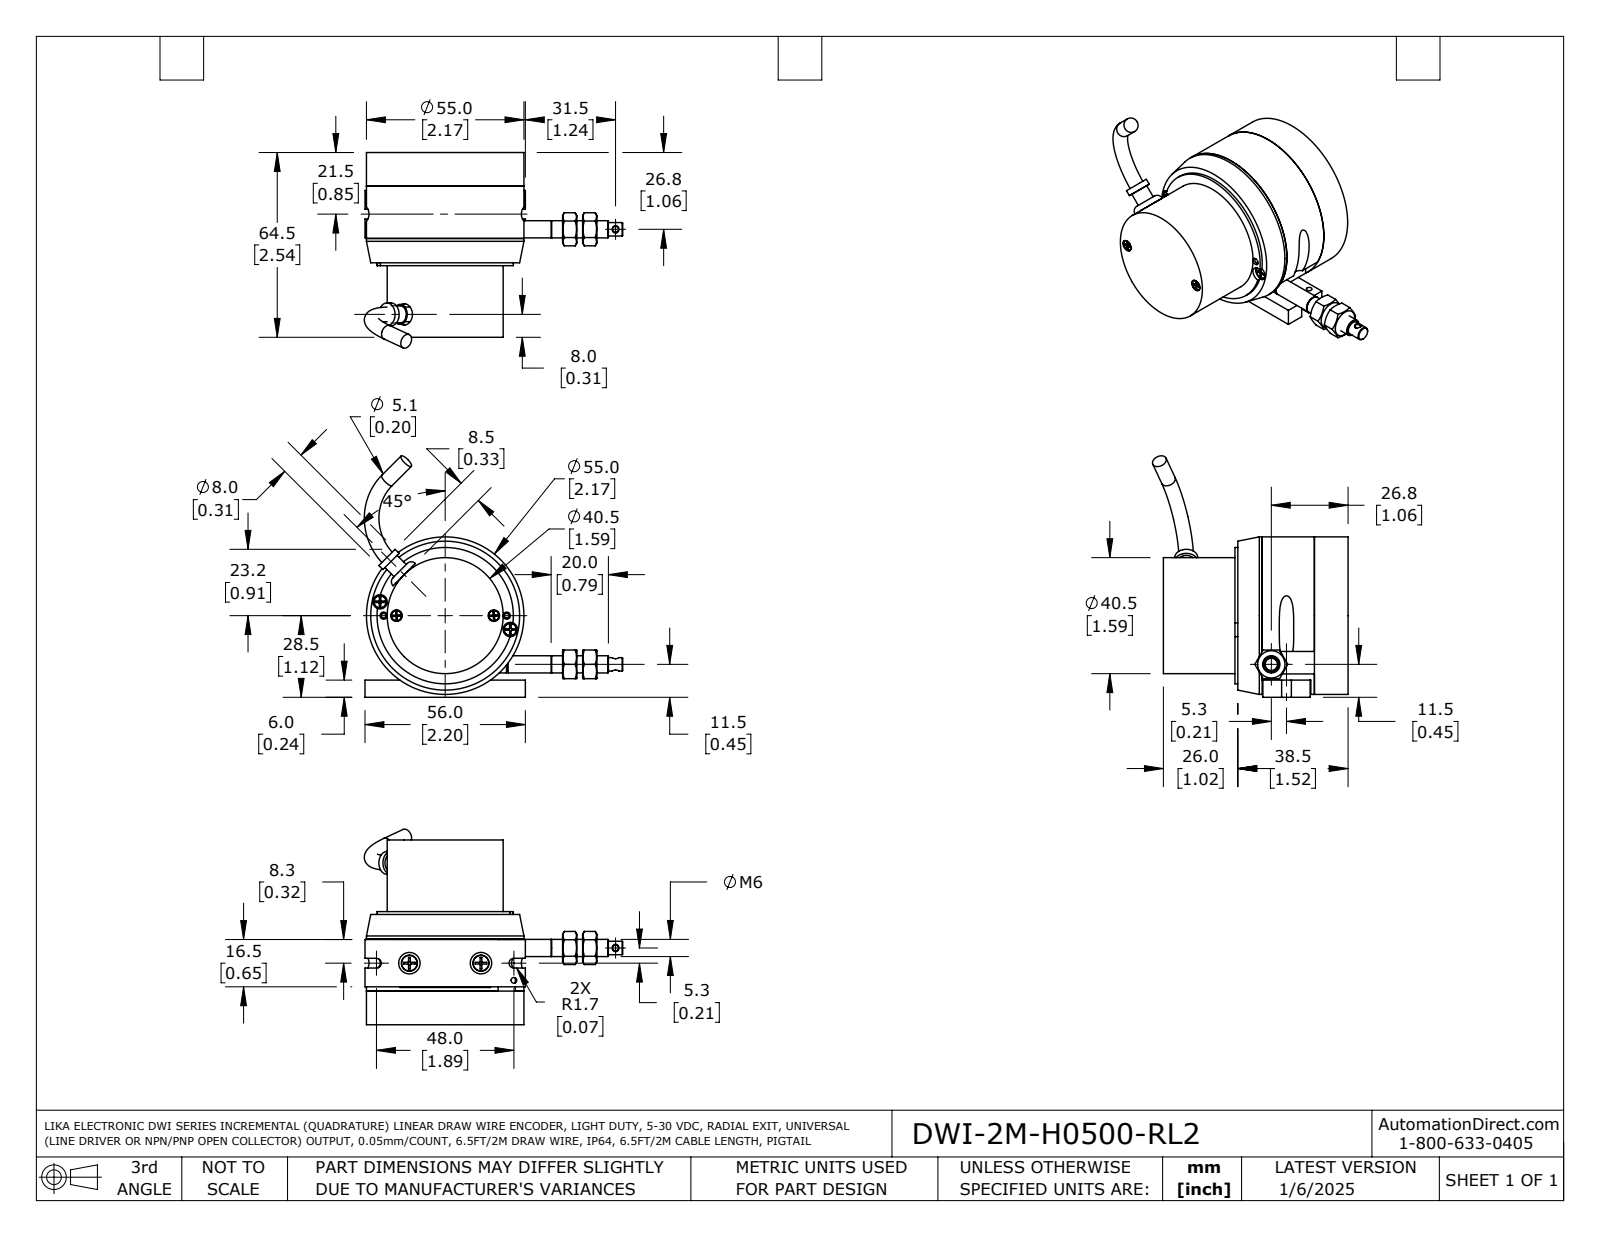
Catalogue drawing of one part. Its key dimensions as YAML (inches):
part_name: "DWI-2M-H0500-RL2"
step_written_by: "SolidWorks 2021 (AUTOMOTIVE_DESIGN)"
units: inches
bodies: {solids: 21, faces: 627, planar: 201, cylindrical: 228, other: 198}
overall_size: [3.553, 3.319, 2.689]
volume: 3.706
surface_area: 61.4
round_holes:
  - {diameter: 0.063, count: 8}
  - {diameter: 0.197, count: 7}
  - {diameter: 0.079, count: 5}
  - {diameter: 0.081, count: 4}
  - {diameter: 0.083, count: 4}
  - {diameter: 0.11, count: 4}
  - {diameter: 0.059, count: 2}
  - {diameter: 0.087, count: 2}
  - {diameter: 0.098, count: 2}
  - {diameter: 0.134, count: 2}
  - {diameter: 0.157, count: 2}
  - {diameter: 0.031, count: 1}
round_bosses_or_shafts:
  - {diameter: 0.098, count: 4}
  - {diameter: 0.118, count: 3}
  - {diameter: 0.236, count: 2}
  - {diameter: 0.201, count: 2}
  - {diameter: 0.079, count: 2}
  - {diameter: 2.165, count: 1}
  - {diameter: 1.874, count: 1}
  - {diameter: 1.594, count: 1}
partial_cylinders:
  - {radius: 0.007, count: 24}
  - {radius: 0.039, count: 14}
  - {radius: 0.008, count: 8}
  - {radius: 0.315, count: 5}
  - {radius: 0.098, count: 3}
  - {radius: 0.067, count: 2}
  - {radius: 0.197, count: 1}
  - {radius: 0.787, count: 1}
face_to_face_distances: [1.181, 0.079, 0.384, 0.463, 0.719, 1.102, 1.093, 2.077, 1.358, 2.539]
hole_center_spacings: [0.196, 0.669, 0.846, 0.946, 1.079, 1.158, 0.098, 0.177]
